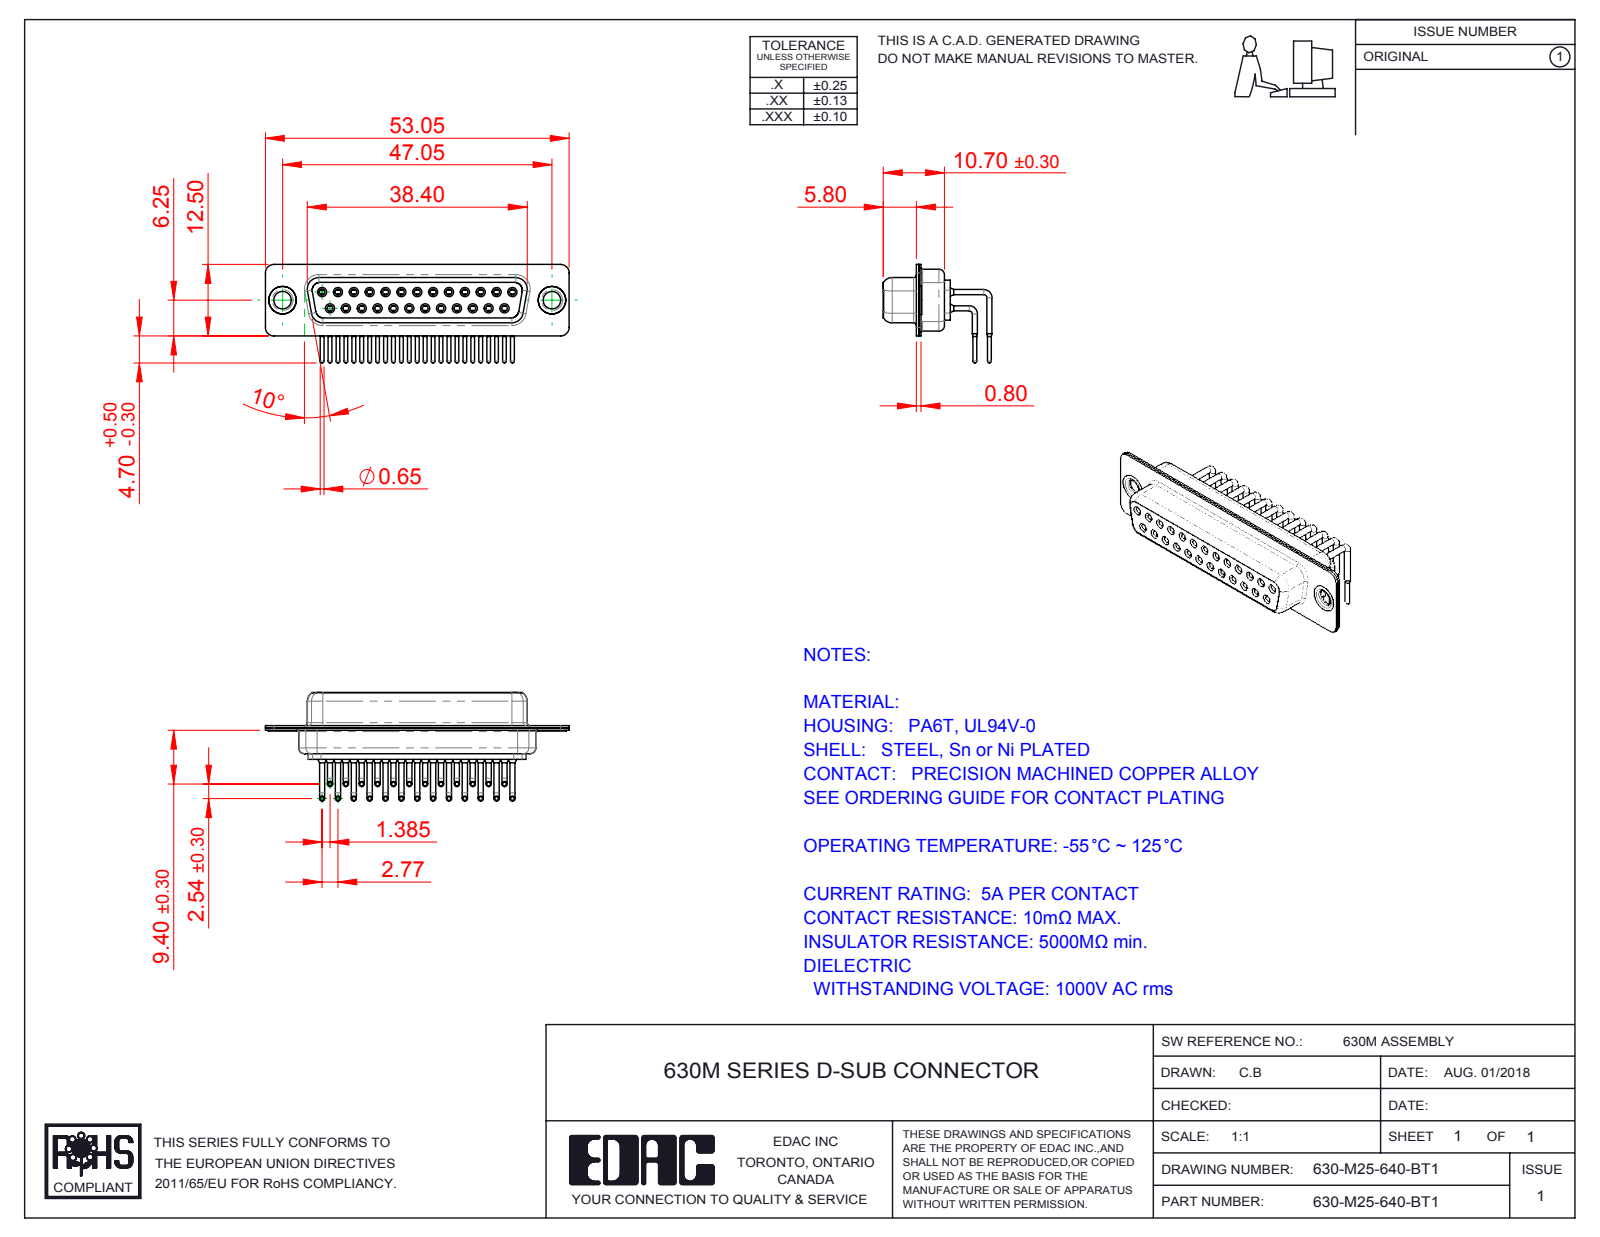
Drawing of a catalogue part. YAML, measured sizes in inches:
part_name: "630M Contact Row 2; 630M Housing_25 Contacts; 630M Shell Front_25 Contacts; 630M Contact Row 1 (+3 more)"
step_written_by: "SolidWorks 2016 (CONFIG_CONTROL_DESIGN)"
units: inches
bodies: {solids: 30, faces: 1578, planar: 442, cylindrical: 696, other: 440}
overall_size: [2.089, 0.748, 0.677]
volume: 0.233
surface_area: 14.85
round_holes:
  - {diameter: 0.039, count: 25}
  - {diameter: 0.043, count: 25}
  - {diameter: 0.067, count: 25}
  - {diameter: 0.071, count: 25}
  - {diameter: 0.079, count: 25}
  - {diameter: 0.12, count: 2}
  - {diameter: 0.157, count: 2}
  - {diameter: 0.189, count: 2}
round_bosses_or_shafts:
  - {diameter: 0.035, count: 50}
  - {diameter: 0.063, count: 25}
  - {diameter: 0.059, count: 25}
  - {diameter: 0.026, count: 25}
  - {diameter: 0.197, count: 2}
  - {diameter: 0.193, count: 2}
  - {diameter: 0.14, count: 2}
partial_cylinders:
  - {radius: 0.059, count: 16}
  - {radius: 0.079, count: 12}
  - {radius: 0.053, count: 10}
  - {radius: 0.063, count: 8}
  - {radius: 0.01, count: 4}
  - {radius: 0.02, count: 4}
  - {radius: 0.024, count: 4}
  - {radius: 0.026, count: 4}
face_to_face_distances: [0.016, 0.057, 0.352, 0.244, 0.075, 0.335, 0.278, 0.018, 0.091, 0.033]
hole_center_spacings: [0.124, 0.109, 0.218, 0.327, 0.436, 0.545, 0.198, 0.295]
